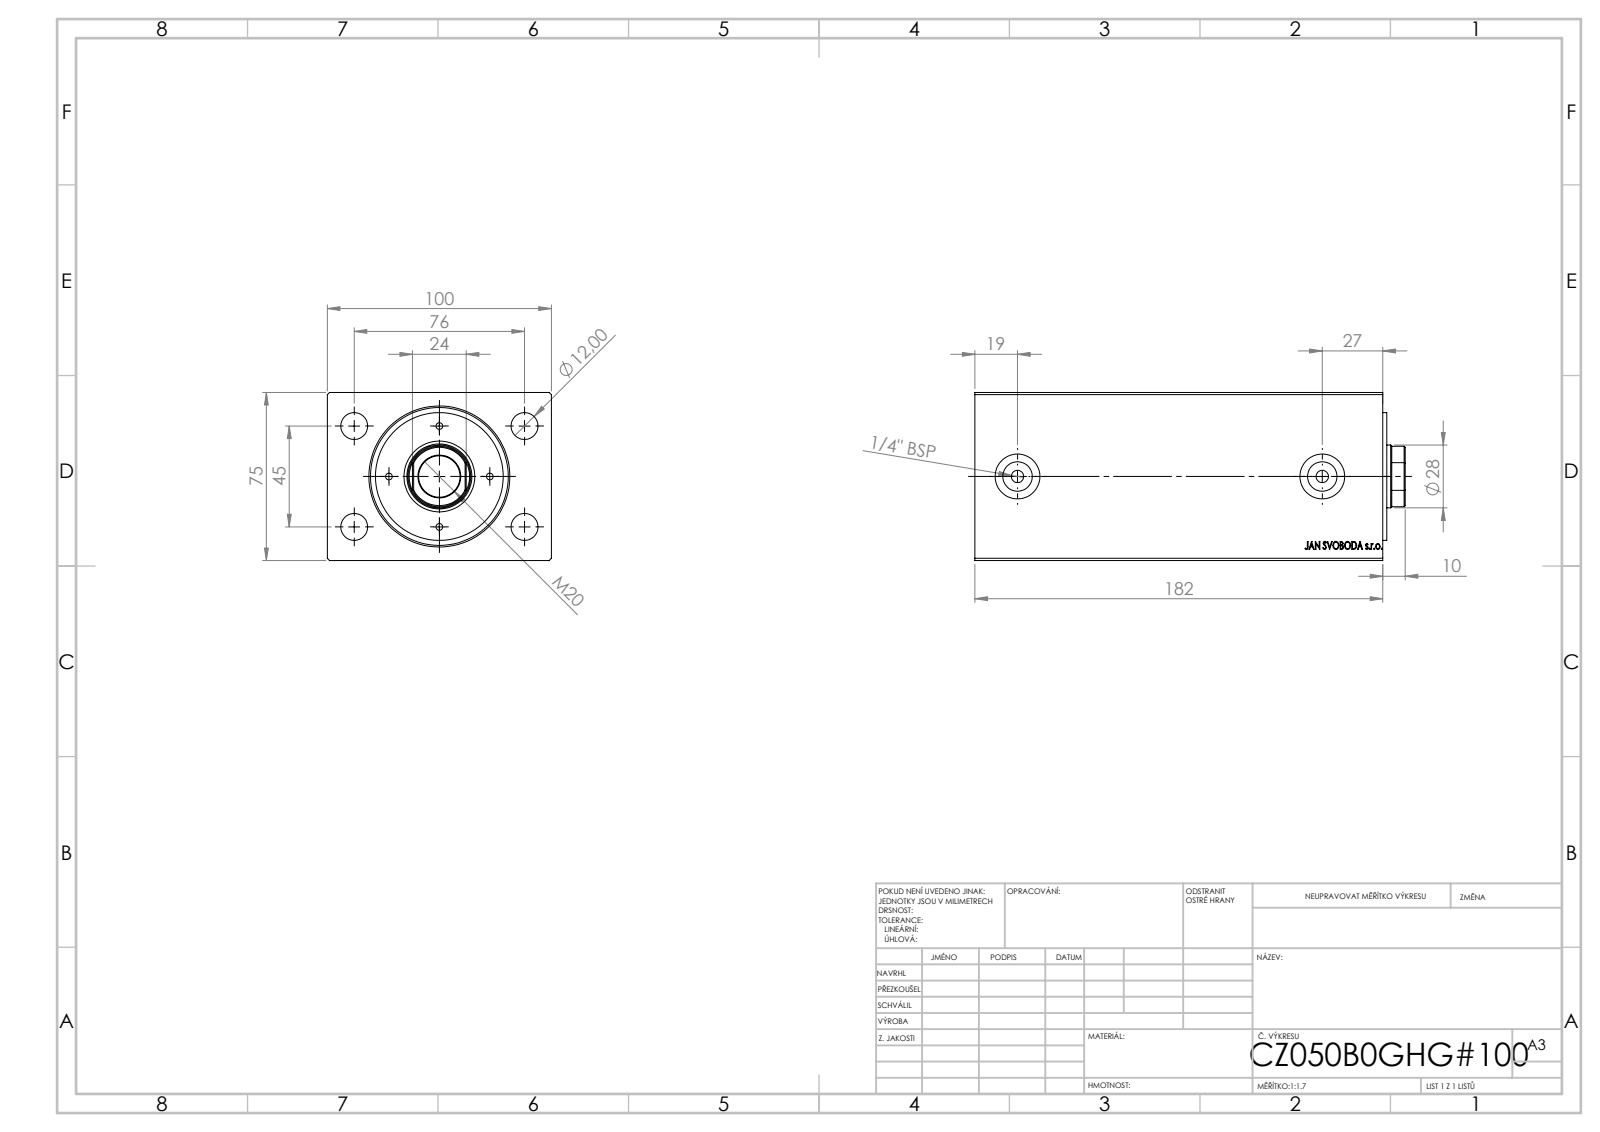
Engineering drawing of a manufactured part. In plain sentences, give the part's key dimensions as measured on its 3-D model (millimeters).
The part is named "V500CZ_B_VC; V500CZ". Its 3-D file was written by "SolidWorks 2019 (CONFIG_CONTROL_DESIGN)". It is 3 solids with 873 faces: 399 planar, 58 cylindrical and 416 other. Overall it measures 192 by 100 by 75 millimeters. Its volume is 1 272 000 cubic millimeters and its surface area 167 412 square millimeters. Round holes: 4 of diameter 3, 4 of diameter 12, 2 of diameter 5.5, 2 of diameter 13.16, 2 of diameter 20, 1 of diameter 18.5, 1 of diameter 28, 1 of diameter 29, 1 of diameter 36, 1 of diameter 50, 1 of diameter 61.5. Round bosses or shafts: 1 of diameter 57. Partial cylindrical surfaces (rounded edges, fillets, slot ends): 1 of radius 13.5. The main face-to-face distances are 75, 100, 182, 164.5, 17.5, 82, 82.5, 1.8, 83.8, 166.3. The hole center spacings are 22.5, 27.32, 31.82, 38, 44.16, 45, 58.9, 64.55.
